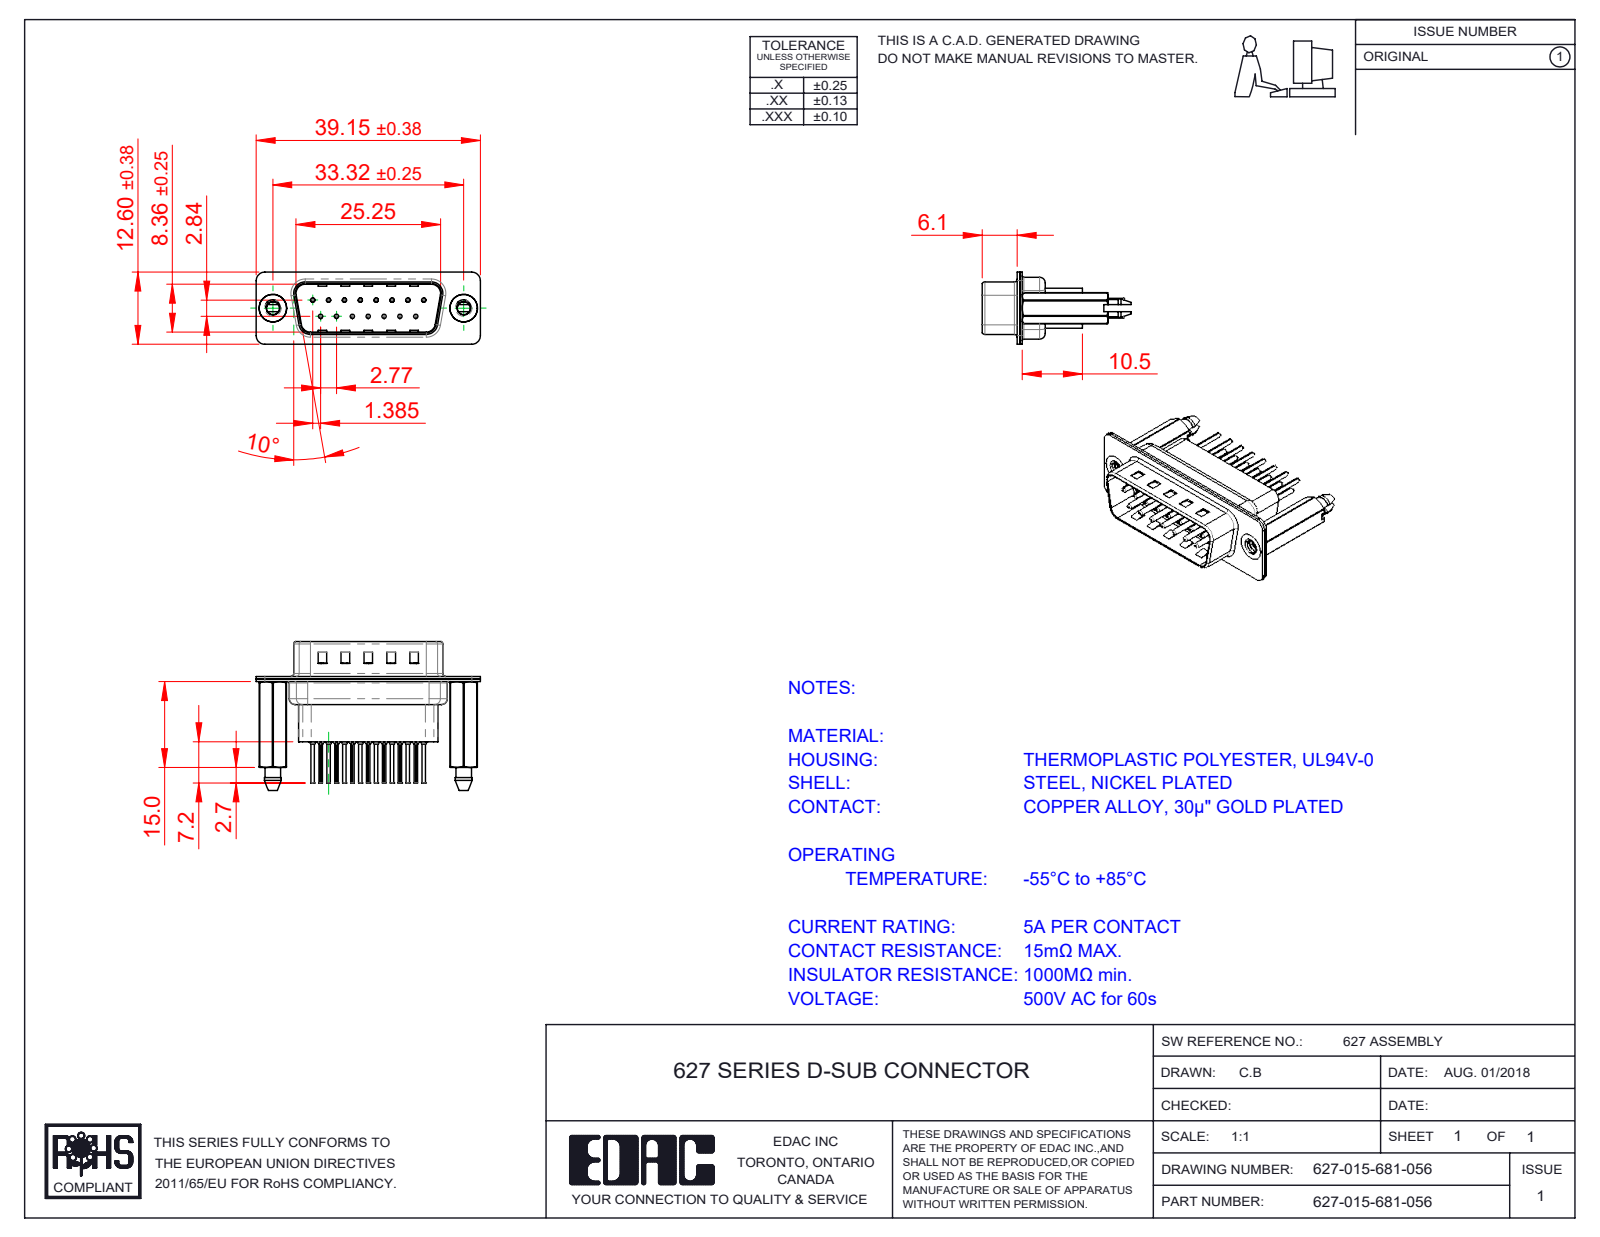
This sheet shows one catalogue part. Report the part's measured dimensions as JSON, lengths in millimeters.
{"part_name": "627-015-681-056; 627 Housing_15 HP; 627 Shell Front_15 Contacts; 627 Contact Row 1_61 (+3 more)", "step_written_by": "SolidWorks 2020 (CONFIG_CONTROL_DESIGN)", "units": "millimeters", "bodies": {"solids": 20, "faces": 1918, "planar": 531, "cylindrical": 754, "other": 633}, "overall_size": [39.15, 25.9, 12.6], "volume_mm3": 2936, "surface_area_mm2": 7555, "round_holes": [[0.2, 15], [0.35, 15], [1.1, 15], [1.6, 15], [2.26, 2], [4, 2], [4.8, 2]], "round_bosses_or_shafts": [[2, 15], [1.5, 15], [0.75, 15], [0.6, 15], [4.9, 2]], "partial_cylinders_radius": [[0.1, 30], [1.5, 18], [2, 12], [1.6, 10], [0.5, 8], [0.25, 4], [0.6, 4], [0.65, 4]], "face_to_face_distances": [0.4, 0.45, 0.9, 0.82, 9.58, 4.76, 1.5, 0.68, 7.68, 1.4], "hole_center_spacings": [3.16, 2.77, 5.54, 8.31, 11.08, 5.03, 5.04, 7.48]}
